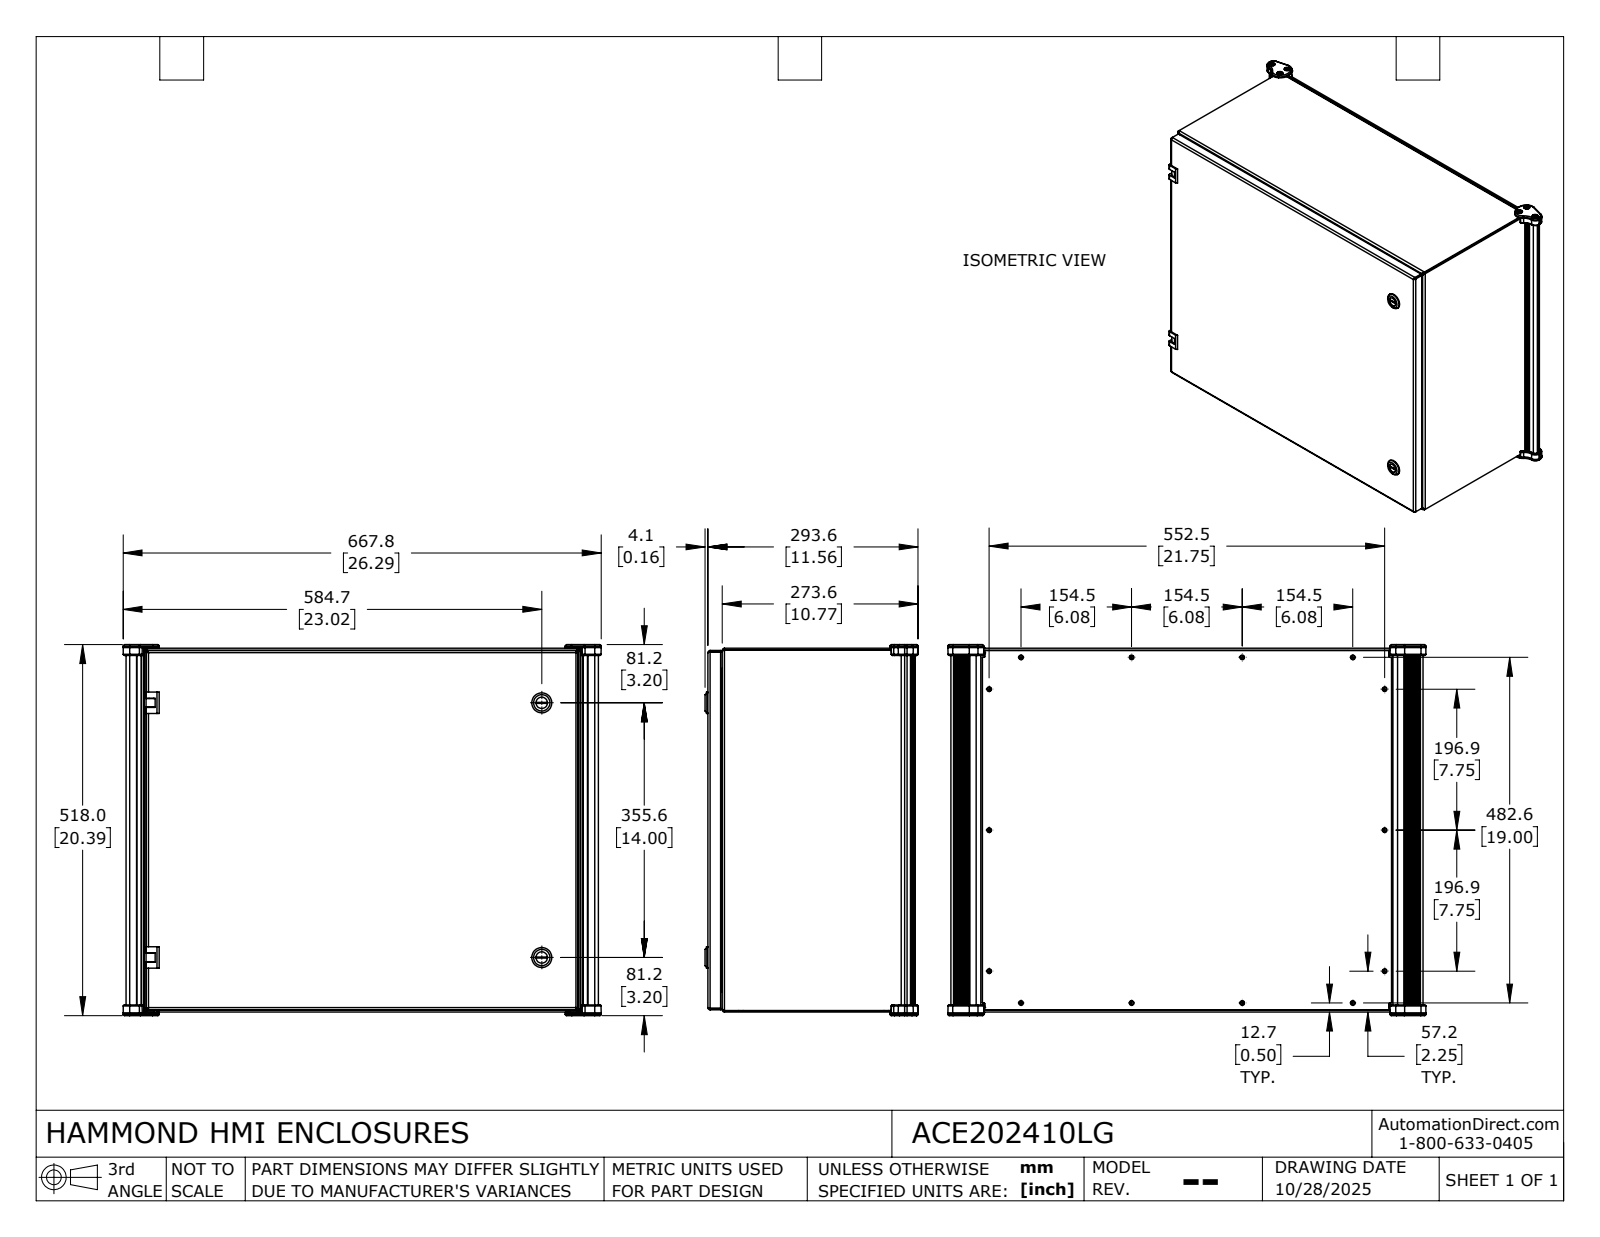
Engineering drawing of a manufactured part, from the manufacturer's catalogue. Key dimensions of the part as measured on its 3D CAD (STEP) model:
Part name (STEP PRODUCT): ACE202410LG
STEP written by: SolidWorks 2024 (AUTOMOTIVE_DESIGN)
Units: millimetres
Bodies: 103 solids, 2572 faces (1232 planar, 875 cylindrical, 465 other)
Overall size (bounding box): 667.82 × 518.03 × 297.66
Volume: 3 989 000 mm³ · Surface area: 3 453 000 mm²
Round holes (diameter × count): ⌀3.97 ×16, ⌀5.94 ×16, ⌀4.83 ×14, ⌀5.2 ×6, ⌀10.5 ×6, ⌀4.98 ×5, ⌀4.04 ×4, ⌀10.32 ×4, ⌀4.06 ×2, ⌀5 ×2, ⌀5.89 ×2, ⌀6.35 ×2
Round bosses / shafts (diameter × count): ⌀6.5 ×14, ⌀6.35 ×6, ⌀4.83 ×6, ⌀3.79 ×6, ⌀5.99 ×5, ⌀9.53 ×4, ⌀8.38 ×4, ⌀27.94 ×2
Partial cylindrical surfaces — rounded edges, fillets, slot ends (radius × count): R0.25 ×38, R1.5 ×30, R1.03 ×20, R3.09 ×20, R0.4 ×16, R0.75 ×16, R1.27 ×16, R1 ×14
Main face-to-face distances: 2.06, 3.18, 275.1, 277.16, 278.28, 280.34, 607.54, 5.23, 2.05, 502.77
Hole centre spacings: 154.52, 506.73, 203.2, 62.86, 196.85, 203.87, 245.36, 289.86
